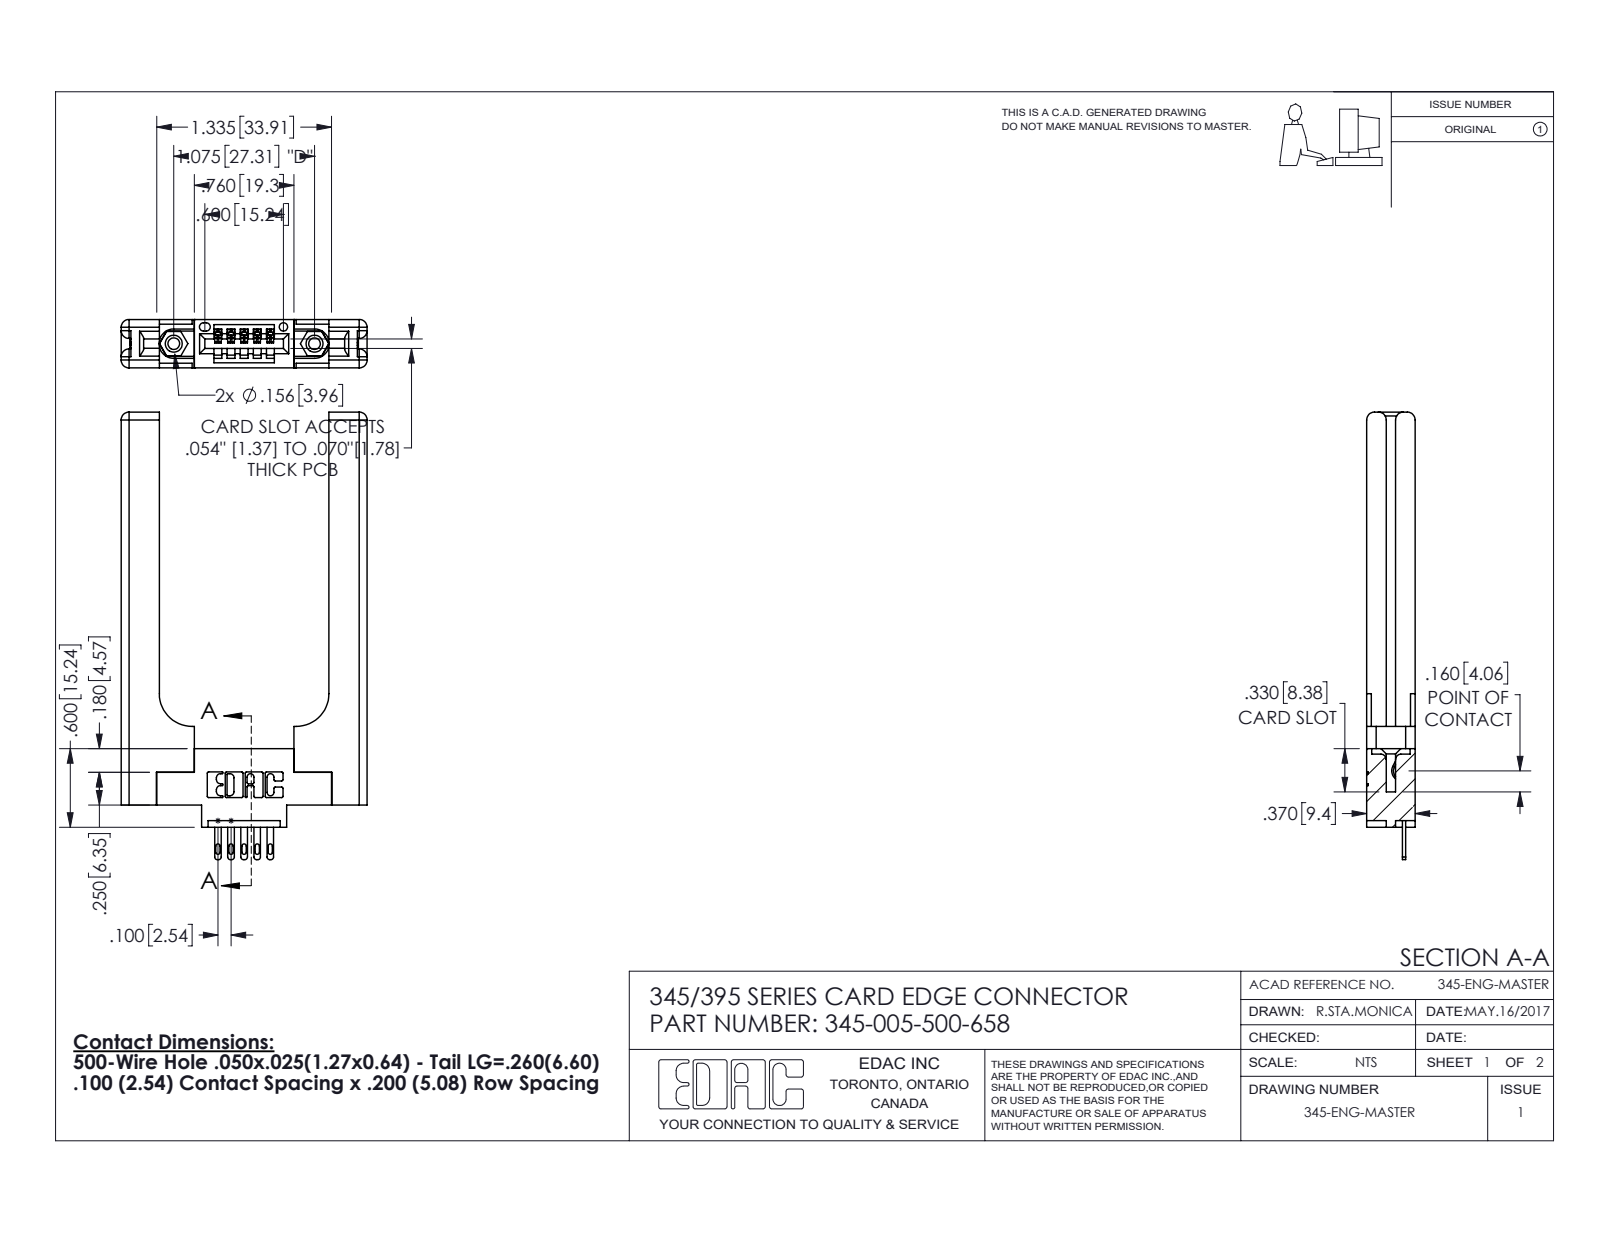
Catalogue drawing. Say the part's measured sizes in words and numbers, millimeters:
The part is named "345-220-058_345-220-058; 345 Part_0.170 Offset - 0.156 Dia-TH; 345-250-001_345-250-001-102; 345-005-500-658 (+1 more)". Its 3-D file was written by "SolidWorks 2016 (CONFIG_CONTROL_DESIGN)". It is 10 solids with 656 faces: 402 planar, 194 cylindrical and 60 other. Overall it measures 86.8 by 47.7 by 9.4 millimeters. Its volume is 12 600 cubic millimeters and its surface area 10 410 square millimeters. Round holes: 2 of diameter 2.3, 2 of diameter 3.2, 2 of diameter 4, 1 of diameter 1.6. Round bosses or shafts: 2 of diameter 3.9. Partial cylindrical surfaces (rounded edges, fillets, slot ends): 22 of radius 0.3, 16 of radius 1.5, 10 of radius 0.2, 10 of radius 0.4, 10 of radius 0.5, 6 of radius 0.2, 6 of radius 0.8, 3 of radius 0.7. The main face-to-face distances are 9.4, 3.8, 5.6, 1.8, 32.9, 3.8, 2, 1.8, 7.6, 7.4. The hole center spacings are 6.9, 21.5, 27.3.
